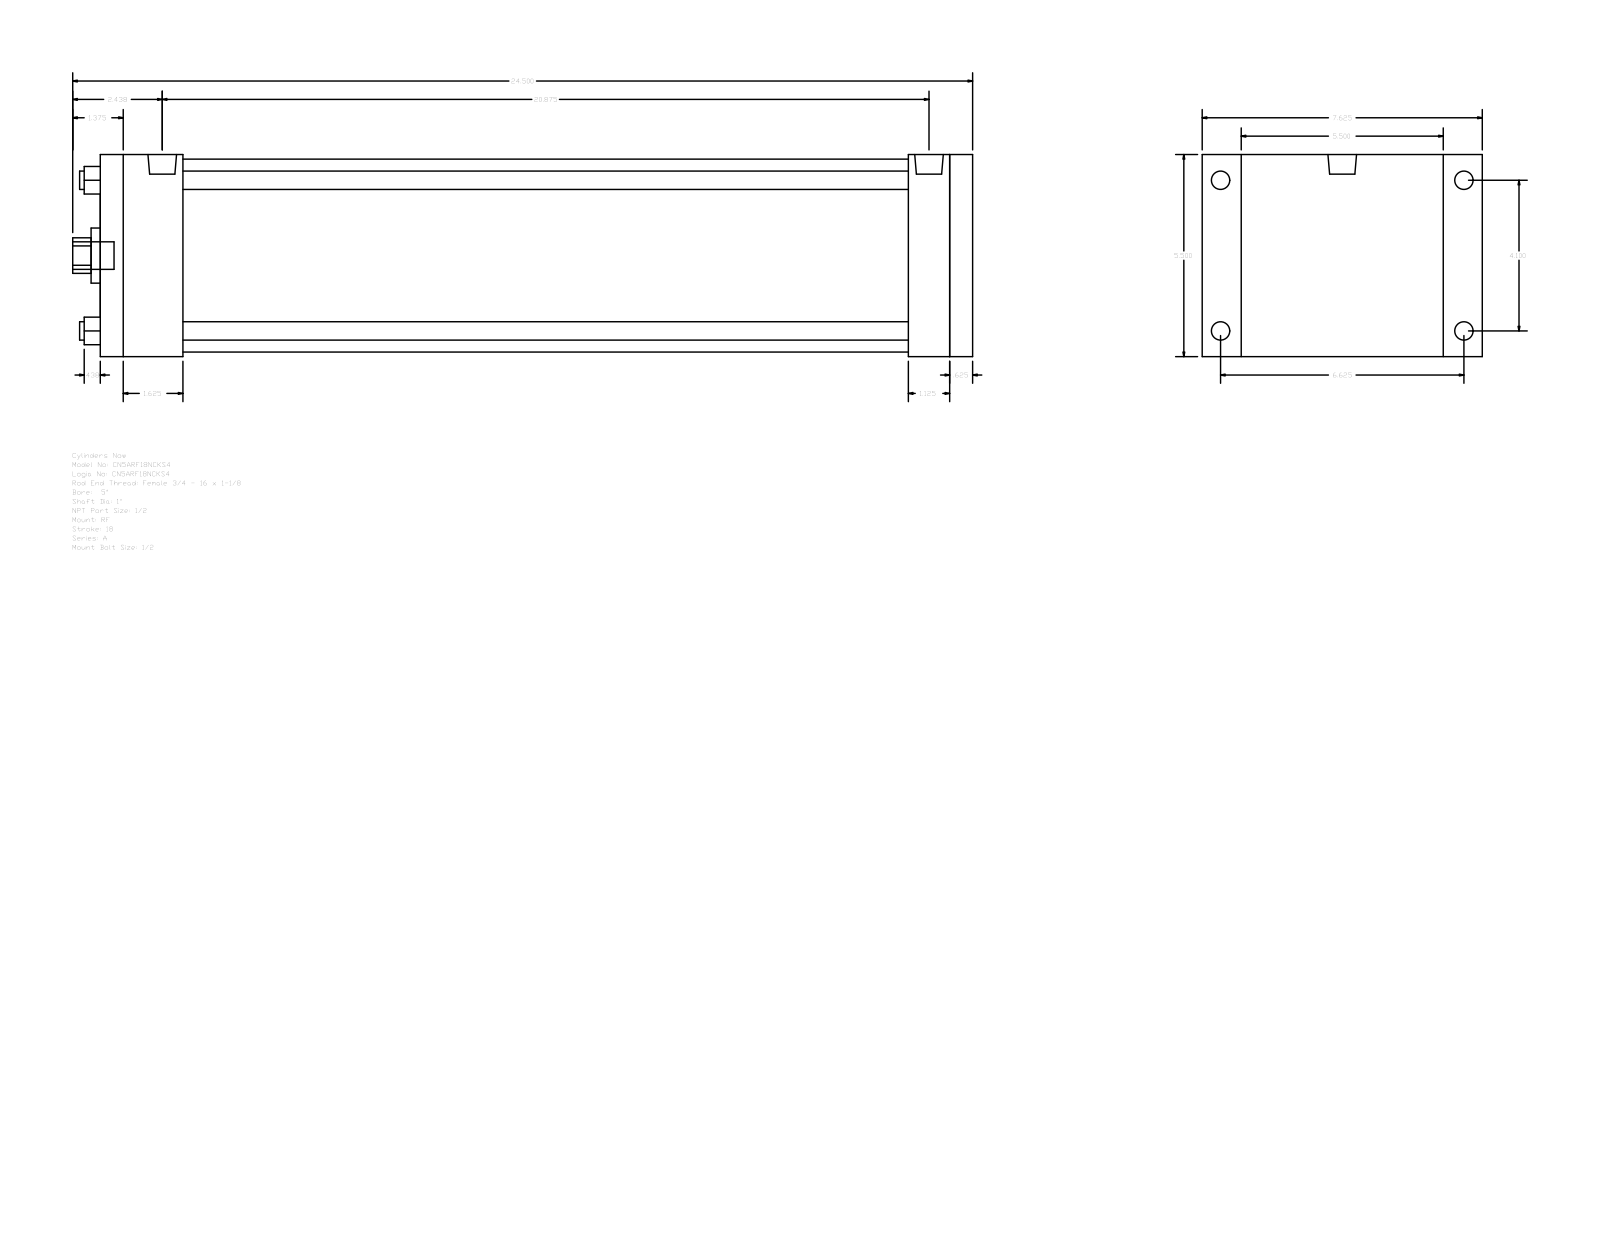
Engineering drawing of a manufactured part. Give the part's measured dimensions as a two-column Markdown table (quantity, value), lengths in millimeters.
| quantity | value |
| --- | --- |
| part name | A_RF__0500_1 |
| STEP written by | GSSL Pune (CONFIG_CONTROL_DESIGN) |
| units | millimeters |
| bodies | 0 solids, 92 faces (64 planar, 28 cylindrical, 0 other) |
| overall size | 622.3 × 193.68 × 139.7 |
| round holes (diameter × count) | 12.7 × 4, 25.4 × 1, 38.1 × 1, 133.35 × 1 |
| round bosses / shafts (diameter × count) | 12.7 × 4, 8.73 × 4, 19.77 × 2, 19.05 × 1 |
| partial cylindrical surfaces (radius × count) | 12.29 × 1 |
| main face-to-face distances | 139.7, 603.25, 587.37, 15.88, 28.57, 57.15, 530.22, 546.1, 558.8, 501.65 |
| hole center spacings | 73.64, 104.14, 147.28 |
